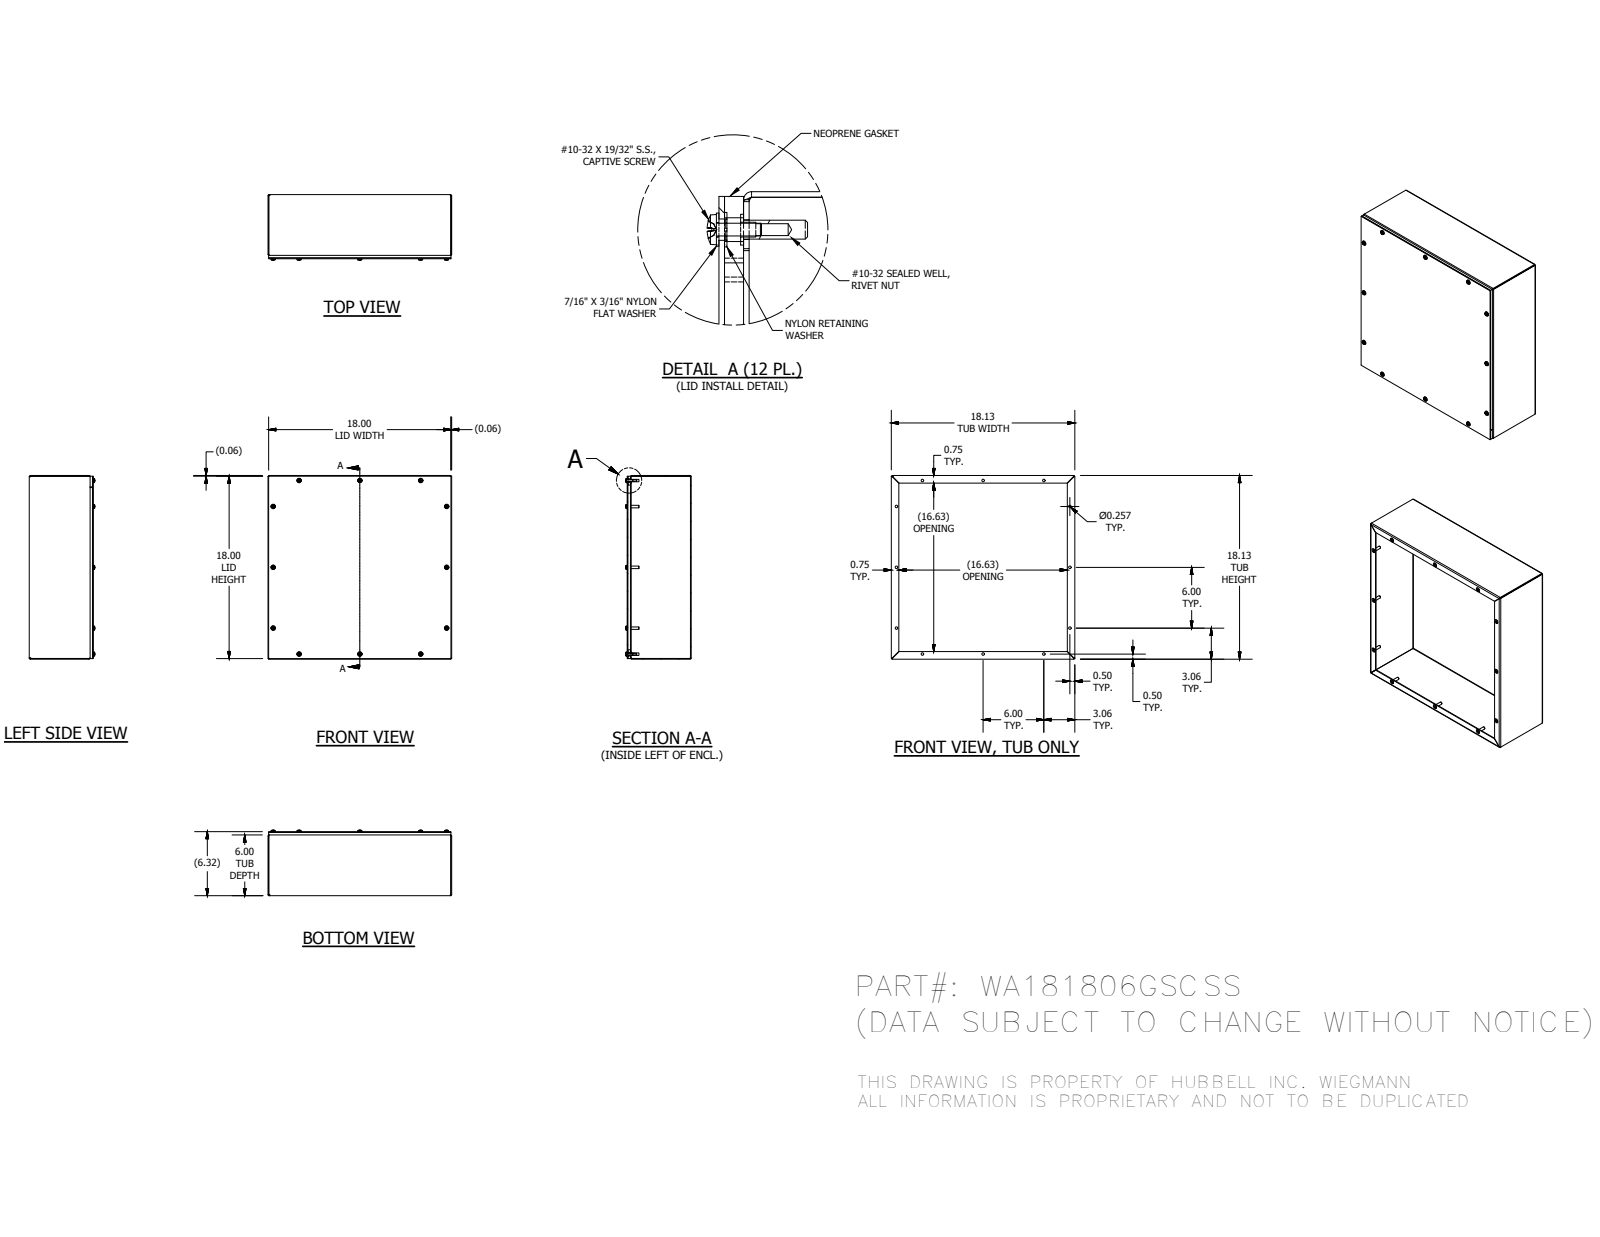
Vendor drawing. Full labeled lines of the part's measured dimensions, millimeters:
Part name (STEP PRODUCT): WA181806GSCSSBKP; WA1818GSCSSLID; 37210; 39035 (+4 more)
STEP written by: Autodesk Inventor 2016 (AUTOMOTIVE_DESIGN)
Units: millimetres
Bodies: 52 solids, 1088 faces (596 planar, 224 cylindrical, 268 other)
Overall size (bounding box): 460.38 × 460.38 × 164.56
Volume: 1 612 000 mm³ · Surface area: 1 576 000 mm²
Round holes (diameter × count): ⌀3.96 ×12, ⌀4.78 ×12, ⌀4.98 ×12, ⌀6.53 ×12, ⌀7.06 ×12, ⌀7.14 ×12, ⌀7.95 ×12
Round bosses / shafts (diameter × count): ⌀11.51 ×12, ⌀11.11 ×12, ⌀10.31 ×12, ⌀6.3 ×12, ⌀4.25 ×12
Partial cylindrical surfaces — rounded edges, fillets, slot ends (radius × count): R0.79 ×12, R2.27 ×12, R1.78 ×8, R2.67 ×8
Main face-to-face distances: 1.88, 158.75, 458.5, 160.63, 156.87, 460.38, 456.62, 150.52, 8.23, 6.35
Hole centre spacings: 152.4, 227, 227.02, 304.8, 375.55, 375.57, 429.08, 460.89
